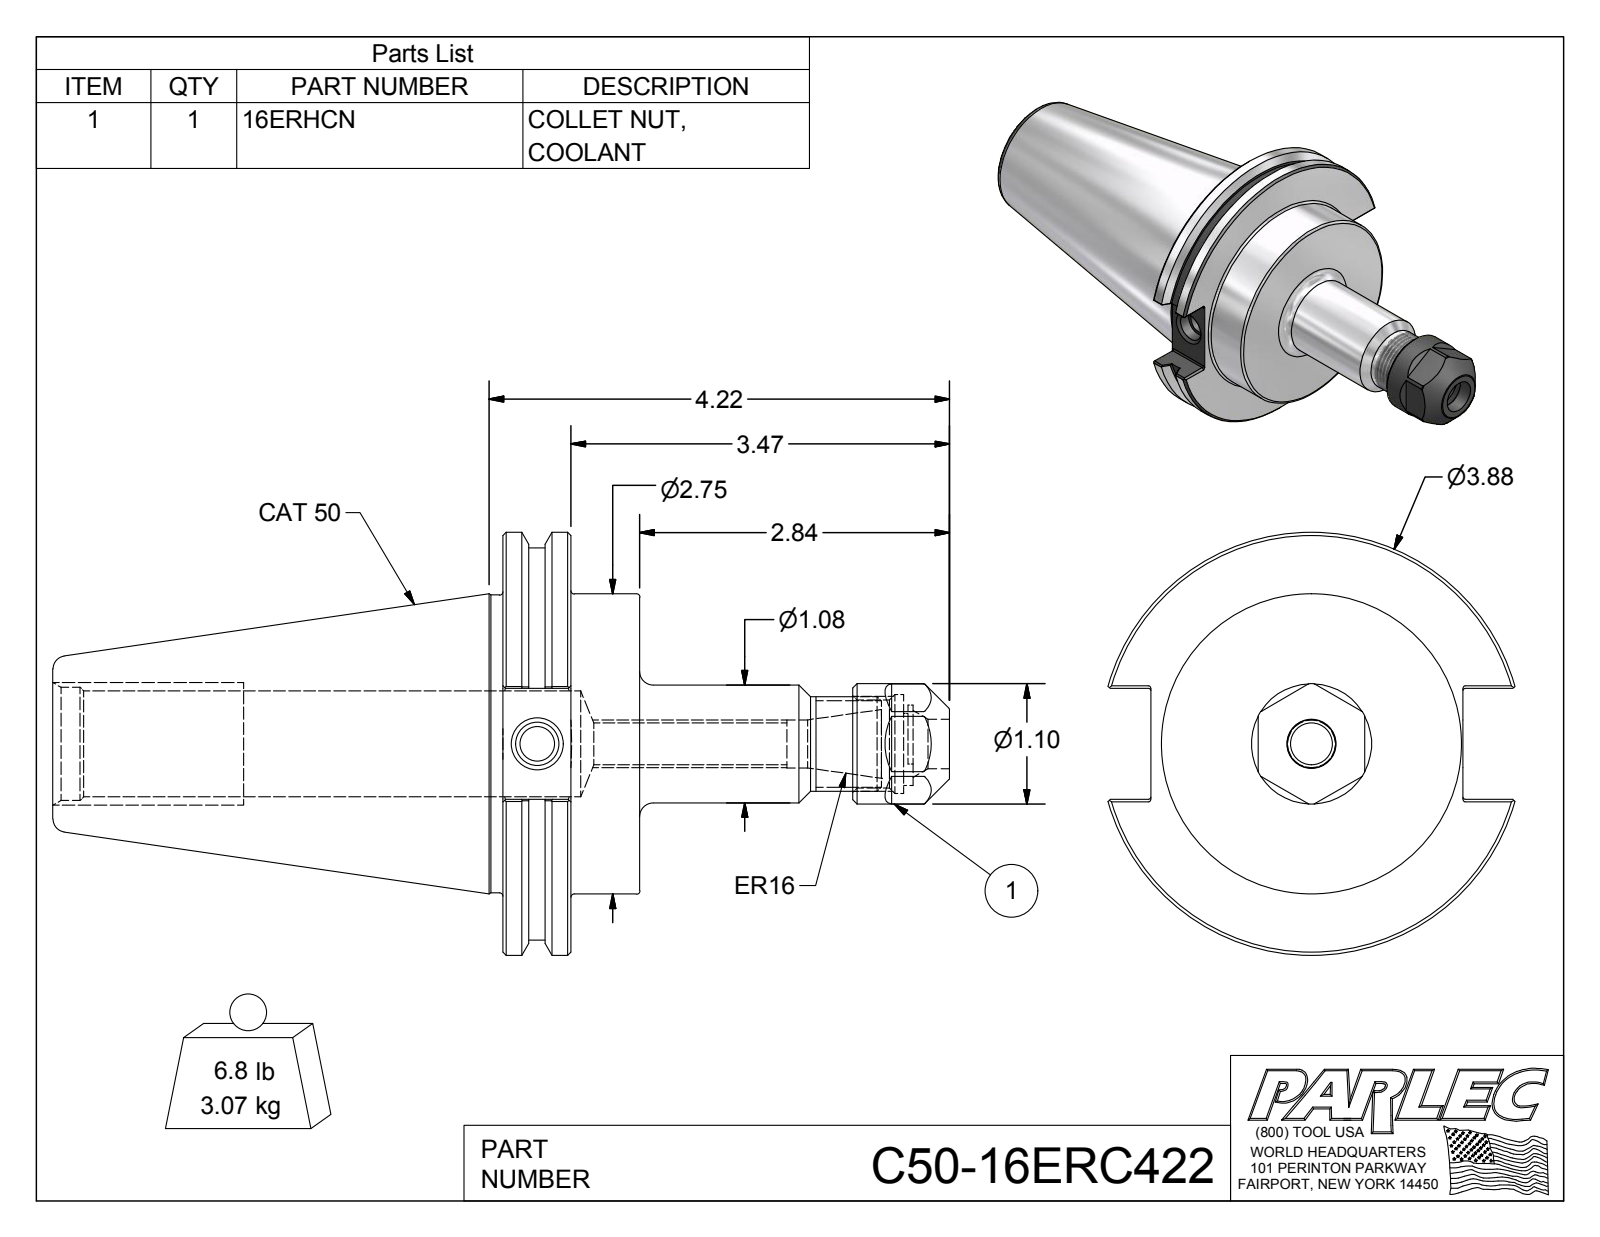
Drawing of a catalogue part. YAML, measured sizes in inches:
part_name: "C50-16ERC422; C50-16ER4-1; 16ERHCN"
step_written_by: "Autodesk Inventor 2012 (AUTOMOTIVE_DESIGN)"
units: inches
bodies: {solids: 2, faces: 128, planar: 50, cylindrical: 34, other: 44}
overall_size: [8.22, 3.875, 3.729]
volume: 24.12
surface_area: 92.14
round_holes:
  - {diameter: 0.315, count: 1}
  - {diameter: 0.383, count: 1}
  - {diameter: 0.399, count: 1}
  - {diameter: 0.44, count: 1}
  - {diameter: 0.453, count: 1}
  - {diameter: 0.661, count: 1}
  - {diameter: 0.807, count: 1}
  - {diameter: 0.906, count: 1}
  - {diameter: 0.97, count: 1}
  - {diameter: 1.038, count: 1}
round_bosses_or_shafts:
  - {diameter: 3.875, count: 1}
  - {diameter: 3.594, count: 1}
  - {diameter: 2.75, count: 1}
  - {diameter: 2.73, count: 1}
  - {diameter: 1.102, count: 1}
  - {diameter: 1.08, count: 1}
  - {diameter: 0.866, count: 1}
partial_cylinders:
  - {radius: 0.02, count: 12}
  - {radius: 0.354, count: 1}
face_to_face_distances: [1.255, 0.625, 0.63, 0.979, 4.125, 4.75, 5.38, 2.86, 1.015, 0.866]
hole_center_spacings: [0.051]
